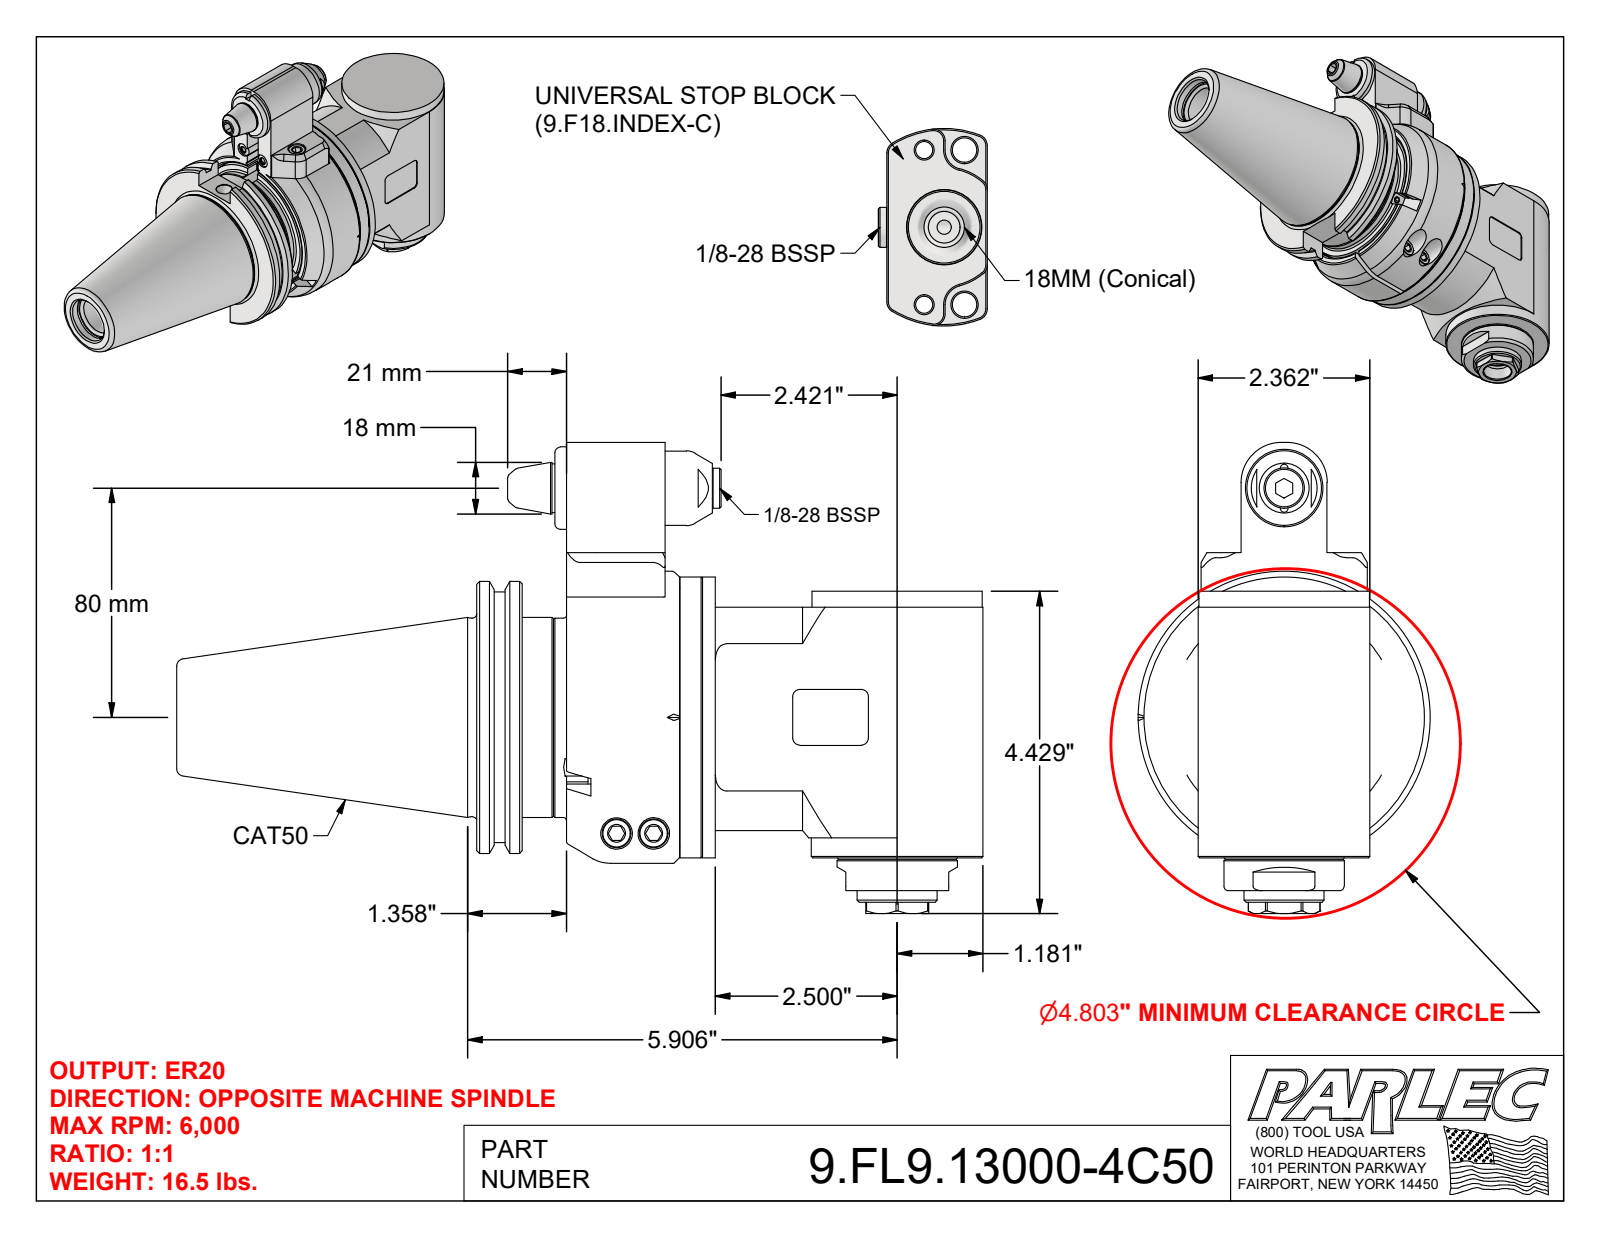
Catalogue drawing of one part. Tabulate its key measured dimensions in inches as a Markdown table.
| quantity | value |
| --- | --- |
| part name | 9.FL9.13000-4C50; 9GA15C_458 (EVO, Type 1, Cat50, 80mm, Conical); 9_FL9_13000 |
| STEP written by | Autodesk Inventor 2022 (AUTOMOTIVE_DESIGN) |
| units | inches |
| bodies | 4 solids, 522 faces (254 planar, 142 cylindrical, 126 other) |
| overall size | 11.087 × 6.476 × 4.016 |
| volume | 71.81 in³ |
| surface area | 240.1 in² |
| round holes (diameter × count) | 0.197 × 3, 0.102 × 2, 0.13 × 2, 0.165 × 2, 0.256 × 2, 0.315 × 2, 0.409 × 2, 0.433 × 2, 1.142 × 2, 0.098 × 1, 0.118 × 1, 0.236 × 1 |
| round bosses / shafts (diameter × count) | 0.394 × 5, 0.709 × 2, 0.315 × 2, 0.236 × 2, 4.016 × 1, 3.875 × 1, 3.858 × 1, 3.594 × 1 |
| partial cylindrical surfaces (radius × count) | 0.039 × 14, 0.118 × 6, 0.098 × 4, 0.157 × 4, 0.02 × 2, 0.315 × 2, 0.551 × 2, 0.492 × 1 |
| main face-to-face distances | 1.26, 2.362, 1.752, 0.492, 2.656, 2.163, 0.904, 0.039, 3.281, 2.789 |
| hole center spacings | 0.276, 0.959, 1.222, 1.49, 1.994, 0.049, 0.512, 0.551 |
